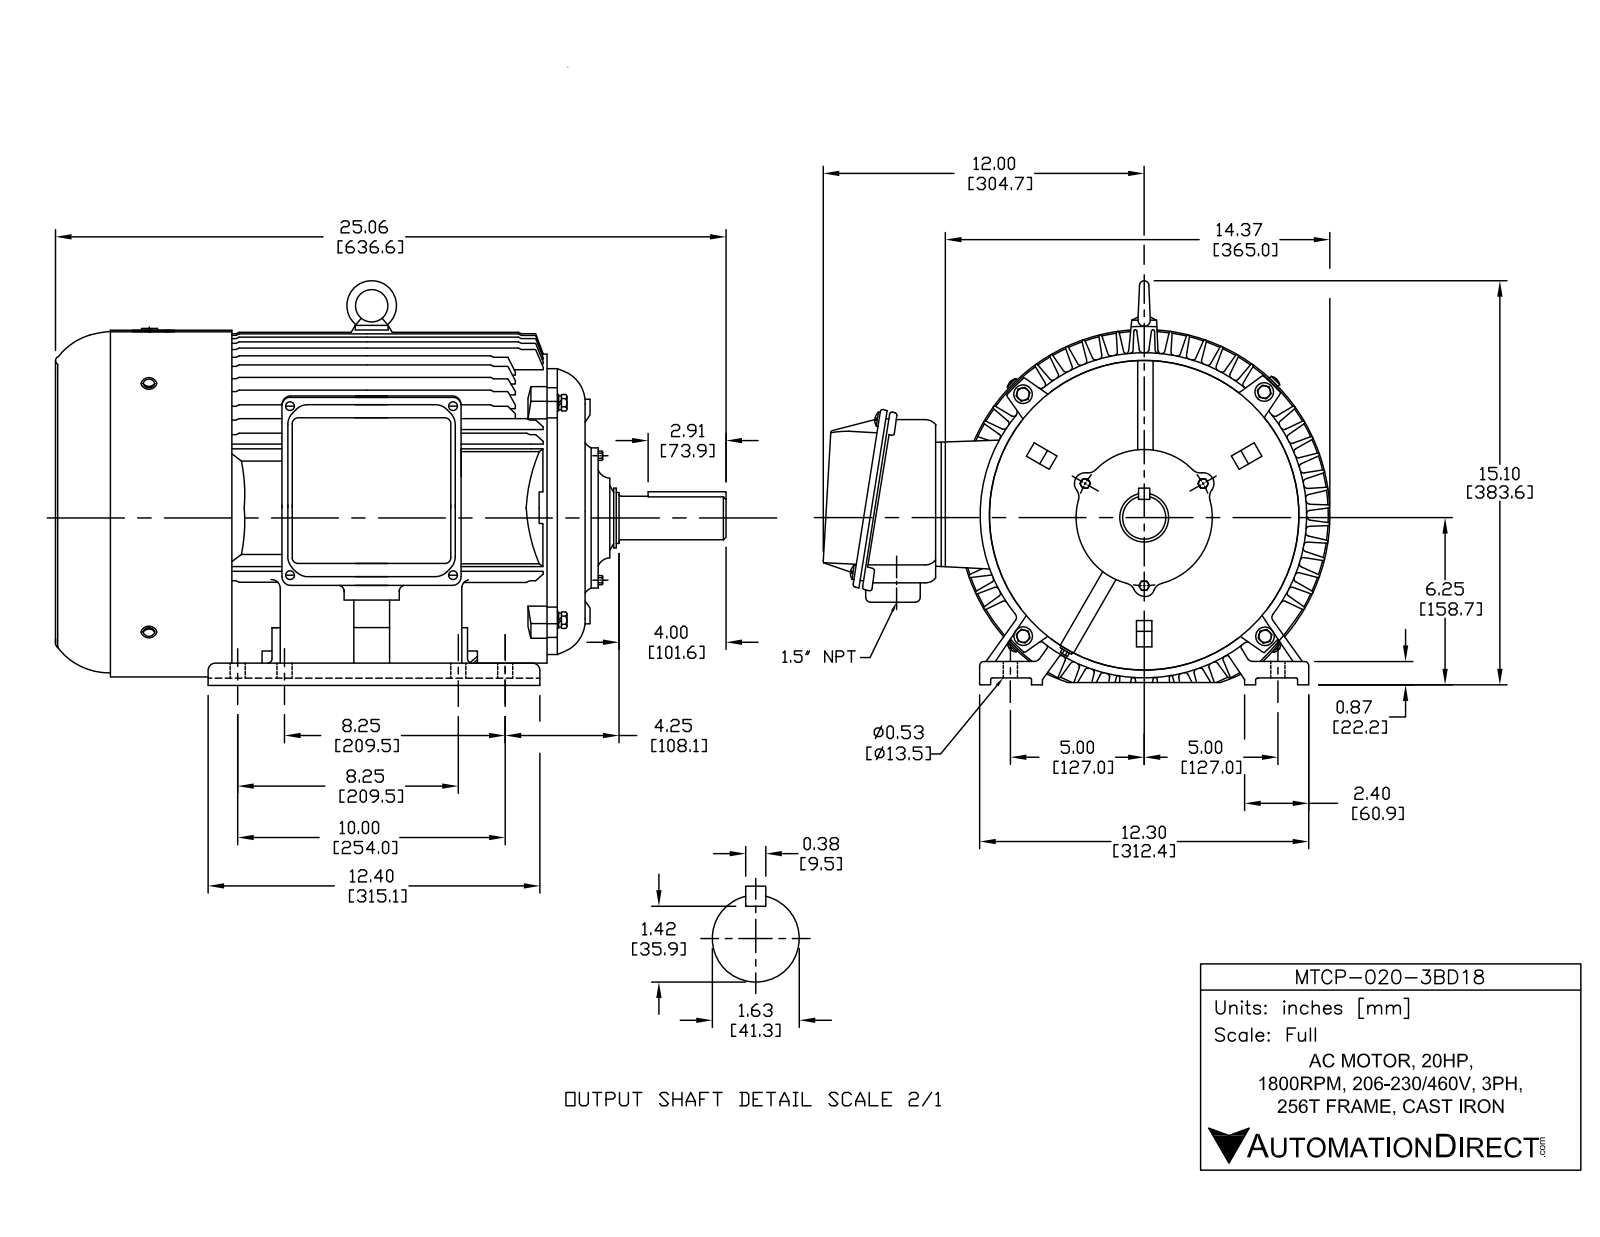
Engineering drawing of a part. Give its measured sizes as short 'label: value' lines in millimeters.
name: hex head bolts-full thread grade c gb_GB_FASTENER_BOLT_HHBFTC M6X12-N; plain washers-chamfered--normal series-a gb_GB_FASTENER_WASHER_SWCA 10; hex head bolts-full thread grade c gb_GB_FASTENER_BOLT_HHBFTC M5X16-N; PE250-280接线盒座_默认_按加工 (+8 more)
written by: SolidWorks 2017 (AUTOMOTIVE_DESIGN)
unit: mm
bodies: 67 solids, 3967 faces (995 planar, 1425 cylindrical, 1547 other)
size: 642.9 × 469.92 × 397.85
volume: 9 000 000 mm³; area: 2 514 000 mm²
holes: 14× ⌀7, 12× ⌀5, 9× ⌀17, 8× ⌀8, 6× ⌀8.5, 4× ⌀2.05, 4× ⌀6.4, 4× ⌀6.68, 4× ⌀9, 4× ⌀10.5, 4× ⌀10.9, 4× ⌀11
bosses: 11× ⌀6, 5× ⌀12, 5× ⌀10, 4× ⌀20, 4× ⌀16.1, 4× ⌀9.88, 2× ⌀5, 1× ⌀355
rounds: 309× R1, 72× R3, 68× R5, 48× R0.5, 36× R1.5, 32× R4, 26× R8, 20× R10
face distances: 5, 1.5, 8, 17, 505.8, 504.3, 10, 513.8, 512.3, 77.94
hole spacings: 75, 57.5, 74.99, 106.06, 254, 144, 44.45, 107.49
